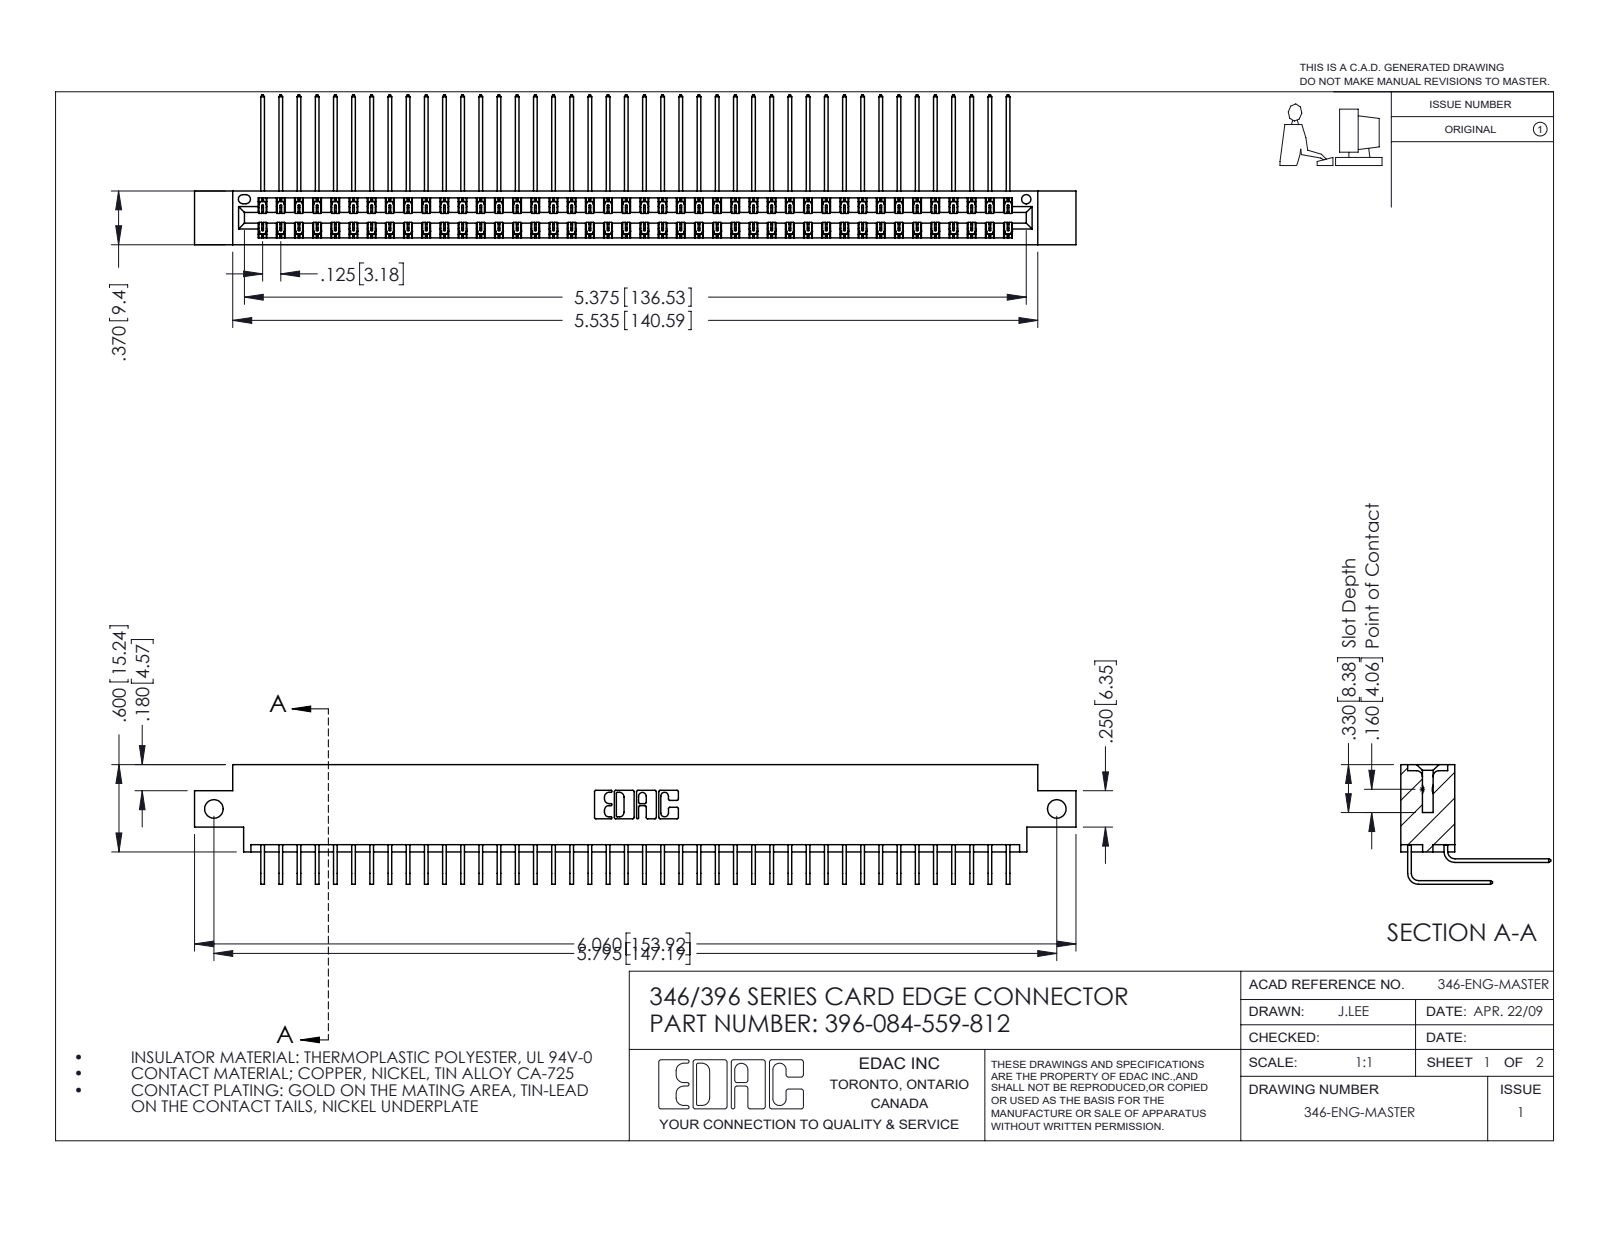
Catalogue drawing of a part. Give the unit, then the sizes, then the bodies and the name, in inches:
Units: inches
Overall size (bounding box): 6.06 × 1.03 × 0.823
Round holes (diameter × count): ⌀0.128 ×2, ⌀0.064 ×1
Partial cylindrical surfaces — rounded edges, fillets, slot ends (radius × count): R0.006 ×126, R0.01 ×22, R0.007 ×6, R0.031 ×6, R0.026 ×3, R0.014 ×2, R0.022 ×2, R0.024 ×2
Main face-to-face distances: 0.048, 0.322, 0.025, 0.37, 0.25, 0.072, 0.298, 0.275, 0.148, 0.222
Hole centre spacings: 5.795
Volume: 0.931 in³ · Surface area: 36.16 in²
Bodies: 85 solids, 4662 faces (3188 planar, 1474 cylindrical, 0 other)
Part name (STEP PRODUCT): 345-292-001_558 559 Tail - 1; 346 Part_0.170 Offset - Side Mount; 396-084-559-812; 345-292-001_559 Tail - 2
STEP written by: SolidWorks 2016 (CONFIG_CONTROL_DESIGN)
